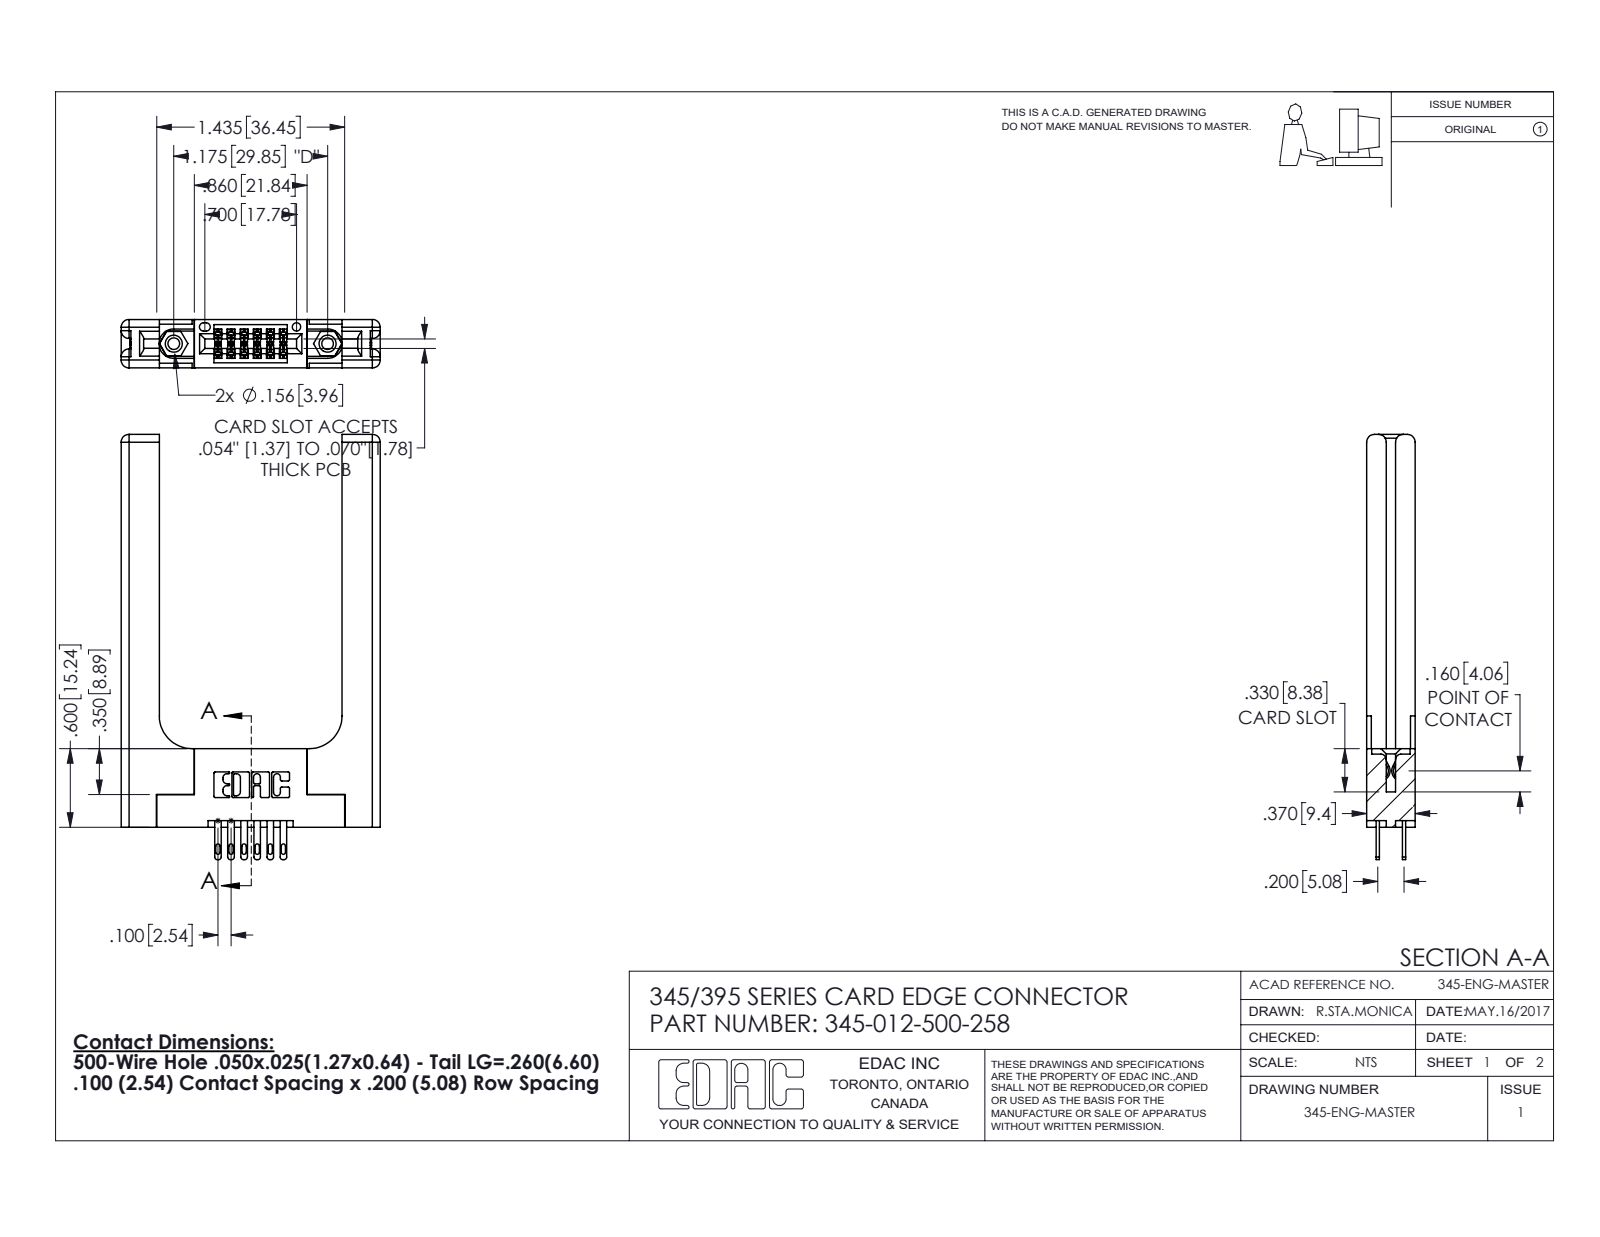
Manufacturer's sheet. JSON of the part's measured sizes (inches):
{"part_name": "345 Part_Flush Mounting Lugs - 0.156 Dia-TH; 345-220-058_345-220-058; 345-292-001_345-293-100; 345-250-001_345-250-001-102 (+1 more)", "step_written_by": "SolidWorks 2016 (CONFIG_CONTROL_DESIGN)", "units": "inches", "bodies": {"solids": 17, "faces": 934, "planar": 552, "cylindrical": 322, "other": 60}, "overall_size": [3.247, 1.979, 0.37], "volume_in3": 0.797, "surface_area_in2": 17.46, "round_holes": [[0.089, 2], [0.125, 2], [0.156, 2], [0.064, 1]], "round_bosses_or_shafts": [[0.155, 2]], "partial_cylinders_radius": [[0.01, 22], [0.006, 18], [0.06, 16], [0.016, 12], [0.02, 12], [0.007, 6], [0.031, 6], [0.026, 3]], "face_to_face_distances": [0.37, 0.15, 0.22, 0.072, 0.077, 0.148, 0.298, 1.396, 0.2, 0.071], "hole_center_spacings": [0.27, 0.946, 1.175]}
